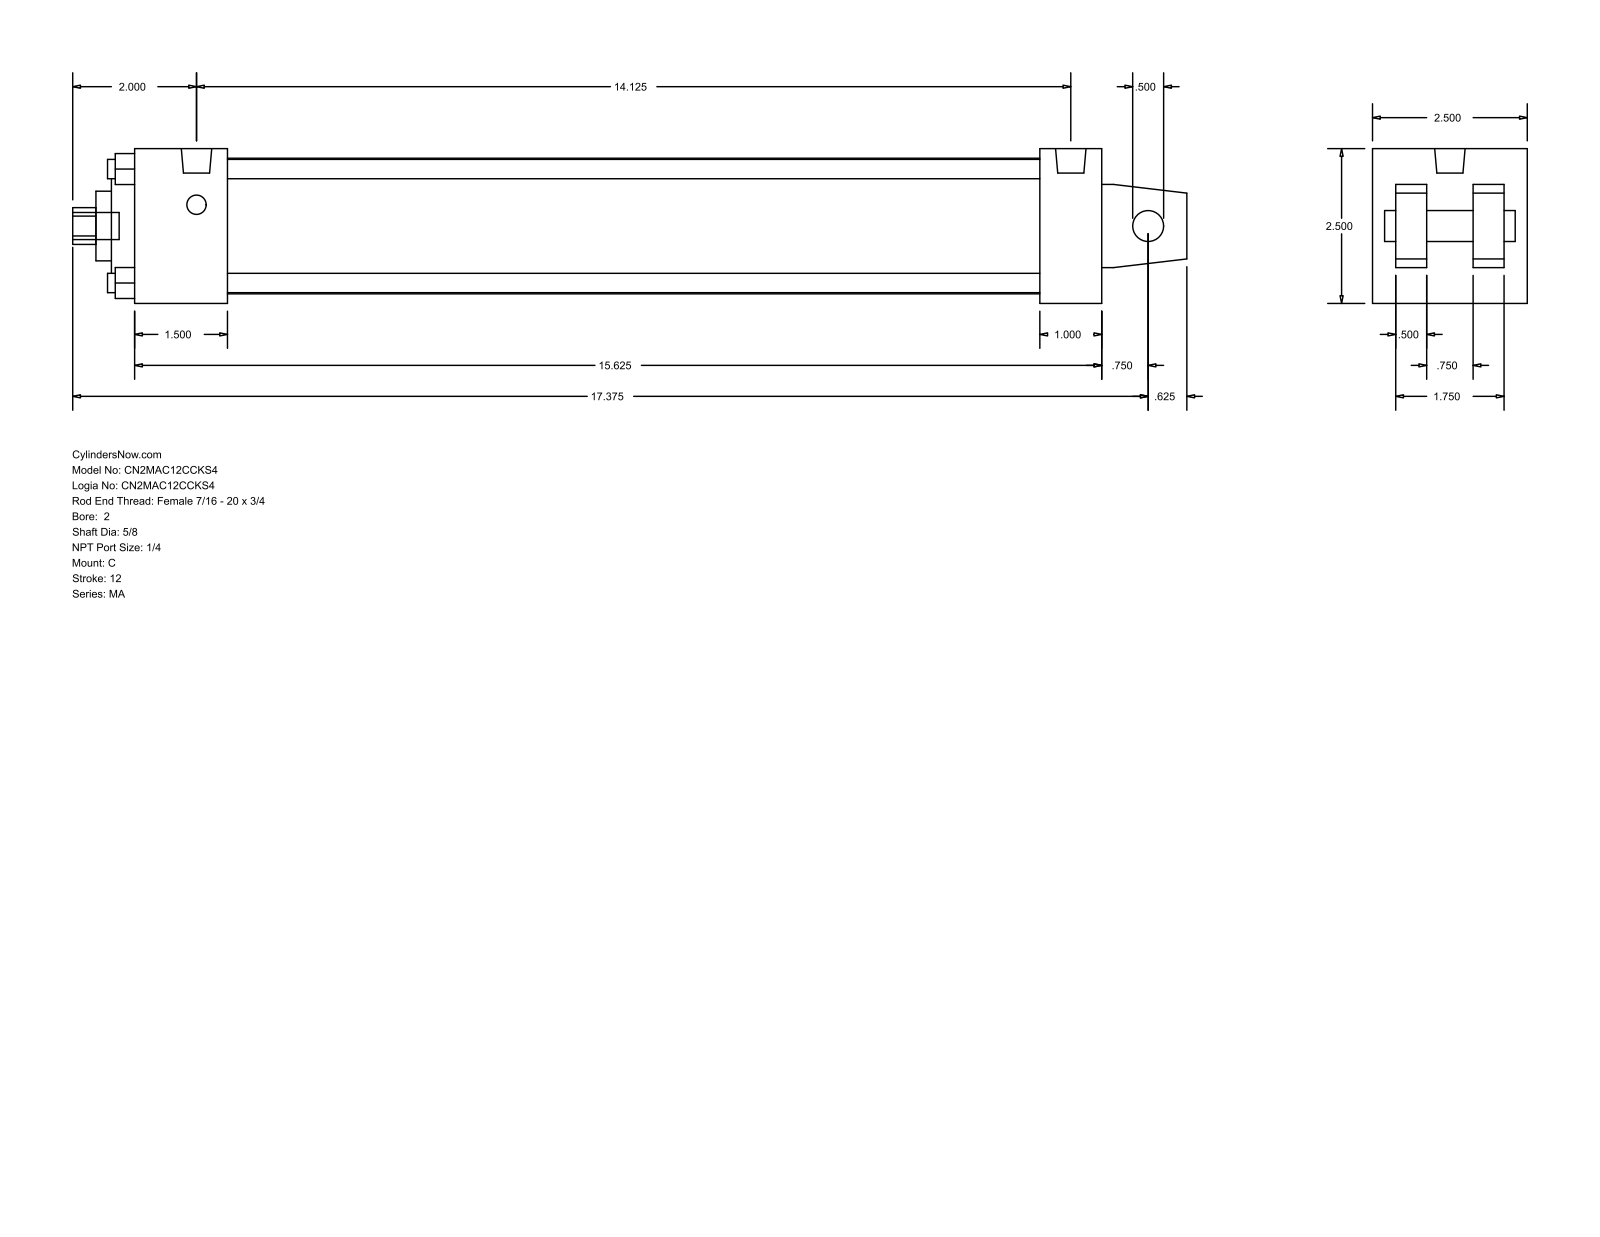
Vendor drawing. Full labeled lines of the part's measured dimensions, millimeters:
Part name (STEP PRODUCT): MA_C__0200_0.625
STEP written by: GSSL Pune (CONFIG_CONTROL_DESIGN)
Units: millimetres
Bodies: 0 solids, 105 faces (77 planar, 28 cylindrical, 0 other)
Overall size (bounding box): 457.2 × 63.5 × 63.5
Round holes (diameter × count): ⌀7.94 ×4, ⌀12.7 ×1, ⌀15.88 ×1, ⌀28.57 ×1, ⌀50.8 ×1, ⌀55.63 ×1
Round bosses / shafts (diameter × count): ⌀7.94 ×4, ⌀12.49 ×2, ⌀11.11 ×1
Partial cylindrical surfaces — rounded edges, fillets, slot ends (radius × count): R7.54 ×1
Main face-to-face distances: 63.5, 9.52, 12.7, 22.22, 41.28, 53.98, 31.76, 38.1, 396.87, 358.77
Hole centre spacings: 33.05, 46.74, 66.1
